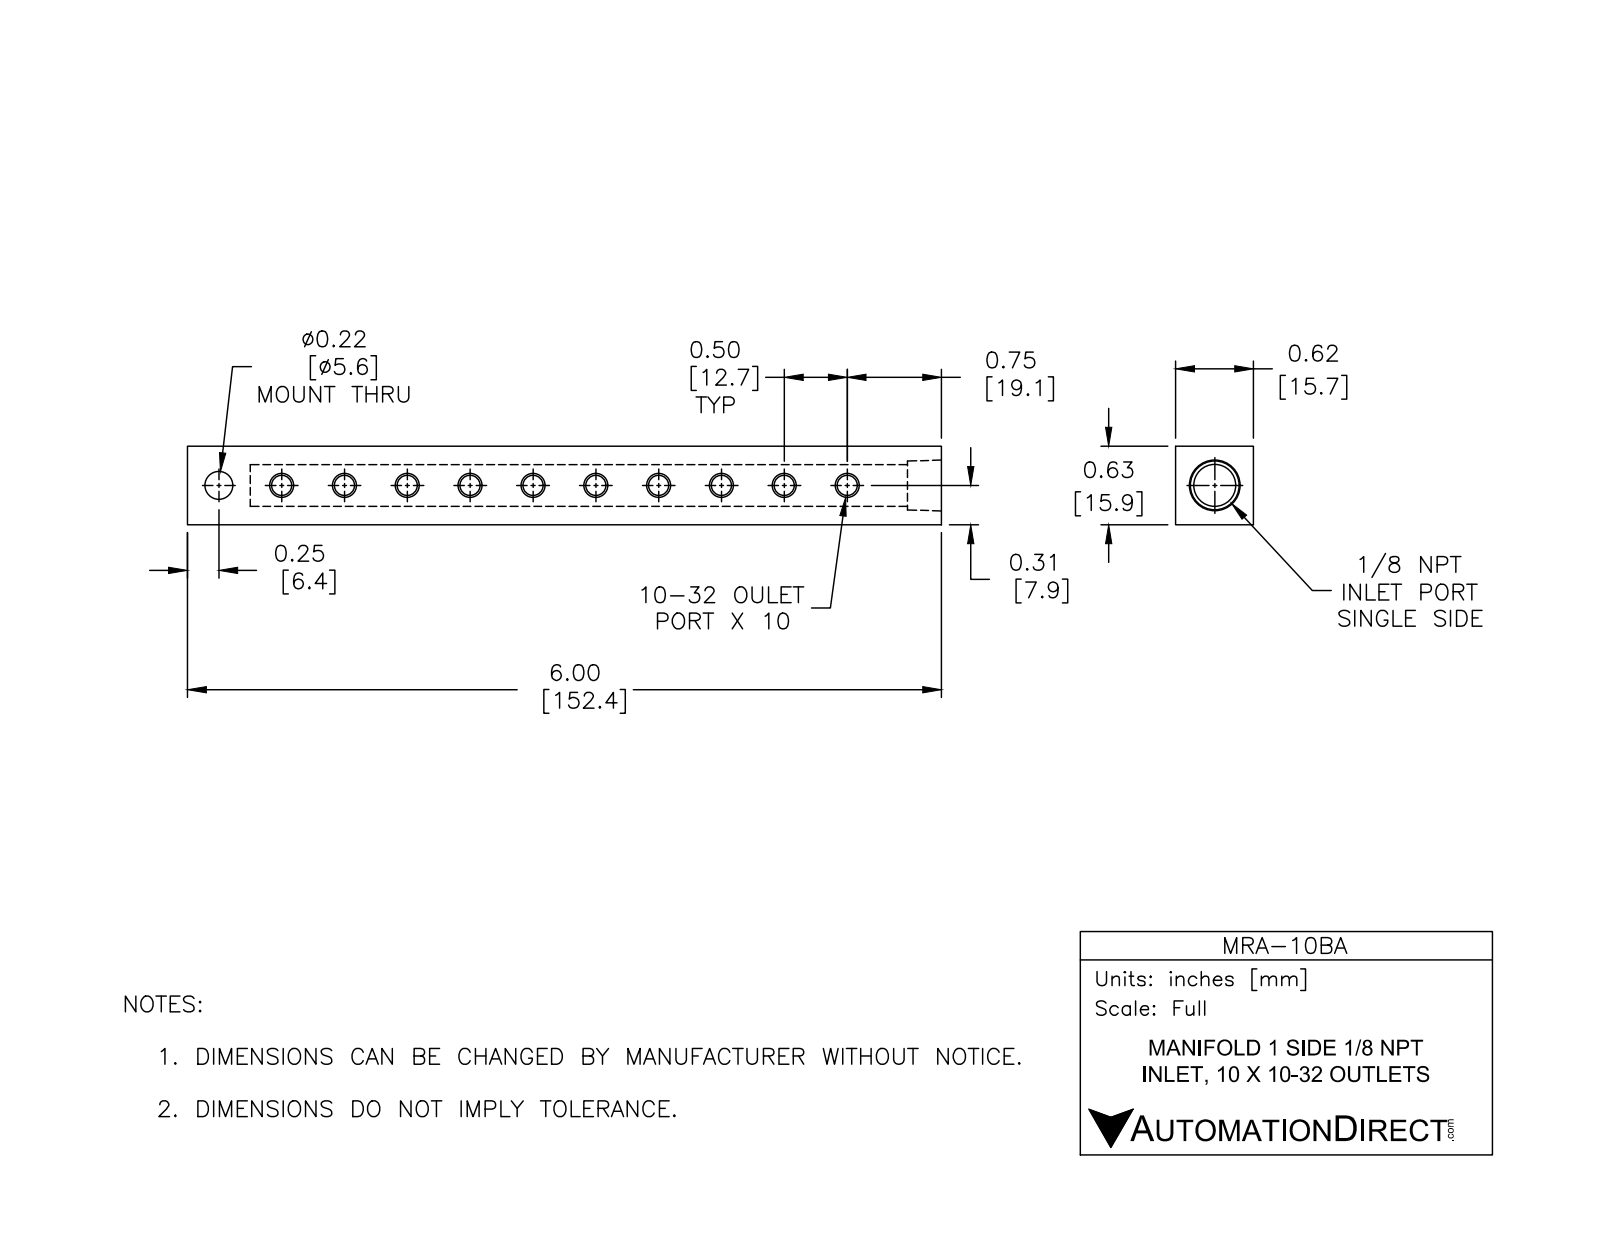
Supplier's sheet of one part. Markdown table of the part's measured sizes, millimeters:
| quantity | value |
| --- | --- |
| part name | MRA-10BA |
| STEP written by | SolidWorks 2015 (CONFIG_CONTROL_DESIGN) |
| units | millimeters |
| bodies | 1 solid, 34 faces (8 planar, 24 cylindrical, 2 other) |
| overall size | 152.4 × 15.9 × 15.7 |
| volume | 29 250 mm³ |
| surface area | 14 340 mm² |
| round holes (diameter × count) | 4 × 10, 5.6 × 1, 8.4 × 1 |
| main face-to-face distances | 15.9, 15.7, 152.4, 12.7, 139.7, 145.5, 132.8, 6.9 |
| hole center spacings | 12.7, 25.4, 38.1, 50.8, 63.5, 76.2, 88.9, 101.6 |
